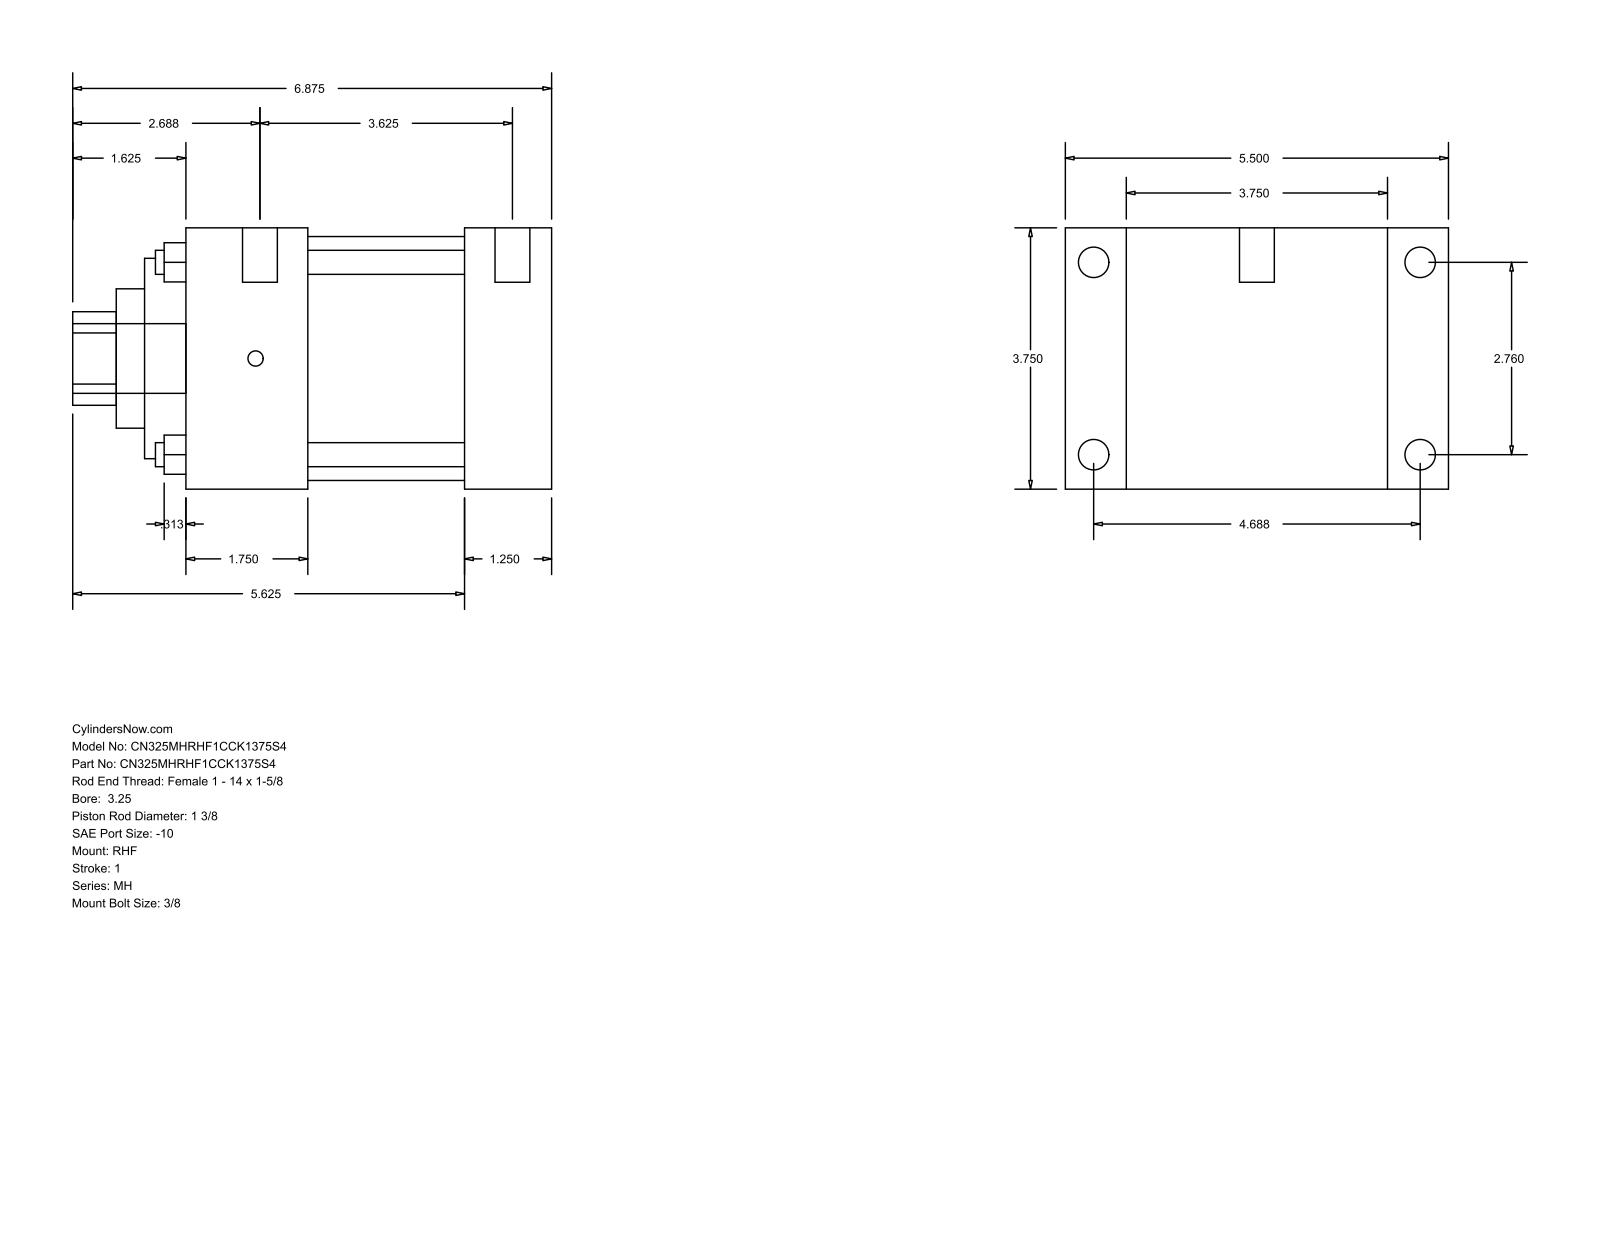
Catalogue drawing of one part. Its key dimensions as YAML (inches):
part_name: "MH_RHF__0325_1.375"
step_written_by: "GSSL Pune (CONFIG_CONTROL_DESIGN)"
units: inches
bodies: {solids: 0, faces: 90, planar: 61, cylindrical: 29, other: 0}
overall_size: [6.875, 5.5, 3.75]
round_holes:
  - {diameter: 0.345, count: 4}
  - {diameter: 1.375, count: 1}
  - {diameter: 2, count: 1}
  - {diameter: 2.875, count: 1}
  - {diameter: 3.5, count: 1}
round_bosses_or_shafts:
  - {diameter: 0.438, count: 4}
  - {diameter: 0.219, count: 4}
  - {diameter: 0.5, count: 2}
  - {diameter: 1, count: 1}
partial_cylinders:
  - {radius: 0.672, count: 1}
face_to_face_distances: [3.75, 1.25, 0.875, 4.625, 4, 5.25, 5.5, 1.75, 2.25, 3.5]
hole_center_spacings: [1.952, 2.76, 3.903]
